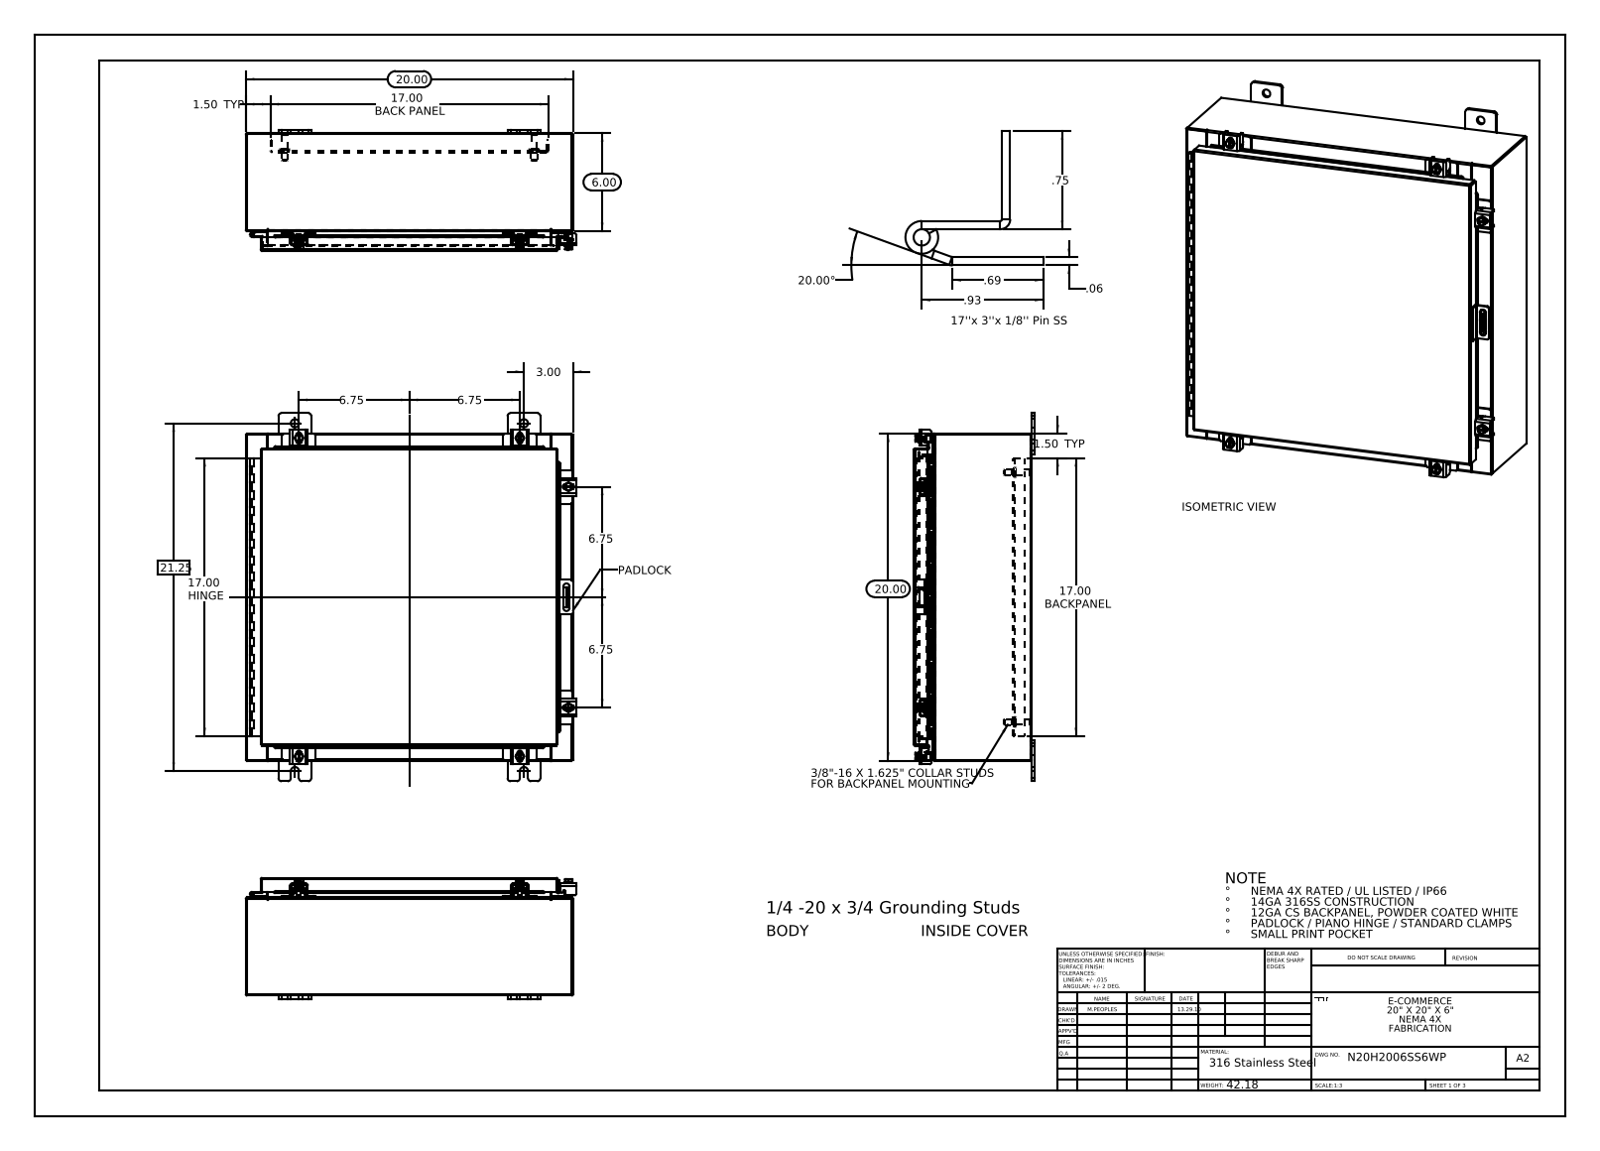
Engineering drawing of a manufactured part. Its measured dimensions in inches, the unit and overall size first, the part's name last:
Units: inches
Overall size (bounding box): 22.5 × 20.211 × 7.389
Round holes (diameter × count): ⌀0.5 ×8, ⌀0.213 ×6, ⌀0.26 ×6, ⌀0.125 ×2, ⌀0.125 ×1
Round bosses / shafts (diameter × count): ⌀0.25 ×7, ⌀0.5 ×6, ⌀0.399 ×6, ⌀0.625 ×4, ⌀0.375 ×4, ⌀0.33 ×4
Partial cylindrical surfaces — rounded edges, fillets, slot ends (radius × count): R0.06 ×30, R0.013 ×25, R0.19 ×24, R0.088 ×21, R0.12 ×12, R0.141 ×12, R0.125 ×10, R0.05 ×9
Main face-to-face distances: 0.075, 7.126, 19.925, 7.201, 7.051, 0.104, 1, 1.075, 6.051, 6.126
Hole centre spacings: 17.373, 14.528, 16.742, 22.532, 13.5, 0.431, 0.934, 1.858
Volume: 148.9 in³ · Surface area: 3 740 in²
Bodies: 47 solids, 1613 faces (860 planar, 657 cylindrical, 96 other)
Part name (STEP PRODUCT): N20H2006SS6WP Cover; N20H2006SS6WP Padlock Hasp; N20H2006SS6WP Top; N20H2006SS6WP Mounting Feet (+8 more)
STEP written by: SolidWorks 2013 (CONFIG_CONTROL_DESIGN)
